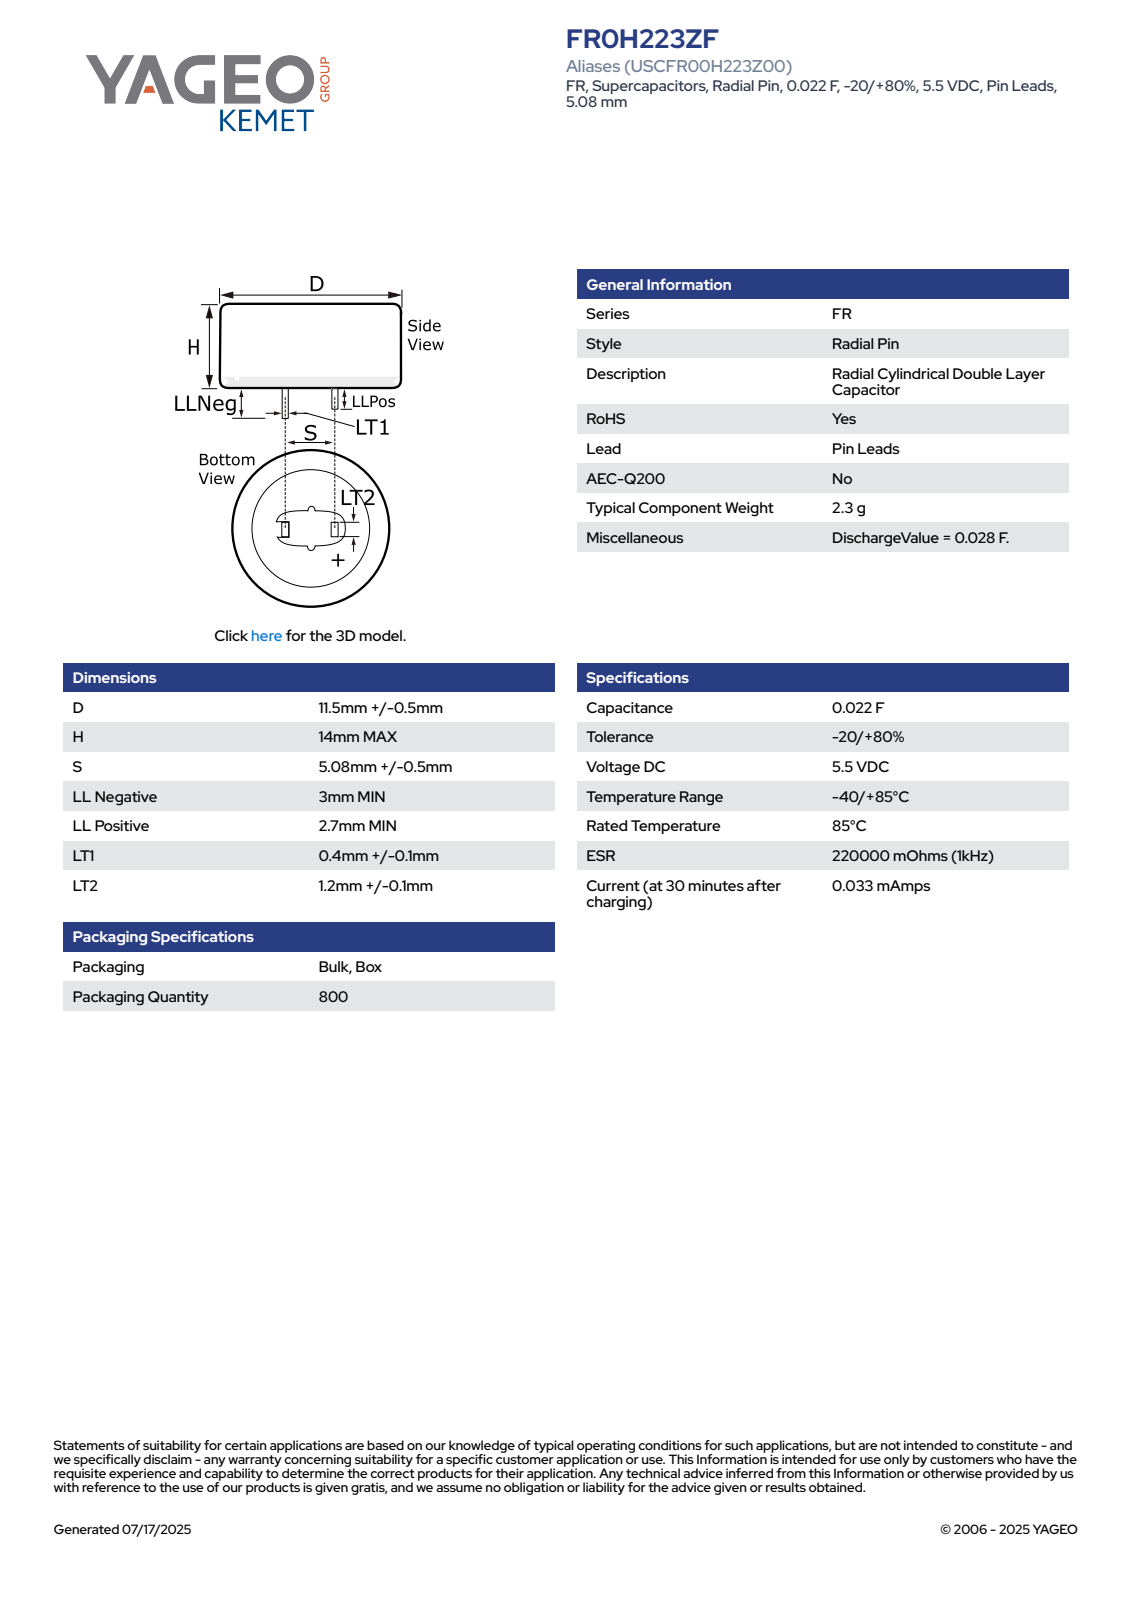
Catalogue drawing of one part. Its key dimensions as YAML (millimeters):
part_name: "CDR_LPLLN_D12L14S5.08LLNEG3LLPOS2.7LT10.5LT21.3"
step_written_by: "SolidWorks 2014 (AUTOMOTIVE_DESIGN)"
units: millimeters
bodies: {solids: 1, faces: 78, planar: 70, cylindrical: 4, other: 4}
overall_size: [17, 12, 12]
volume: 1575
surface_area: 745
round_bosses_or_shafts:
  - {diameter: 12, count: 1}
partial_cylinders:
  - {radius: 6.01, count: 1}
face_to_face_distances: [14, 0.5, 5.08, 5.58, 4.58, 1.3, 2.7, 16.7, 3, 17]
